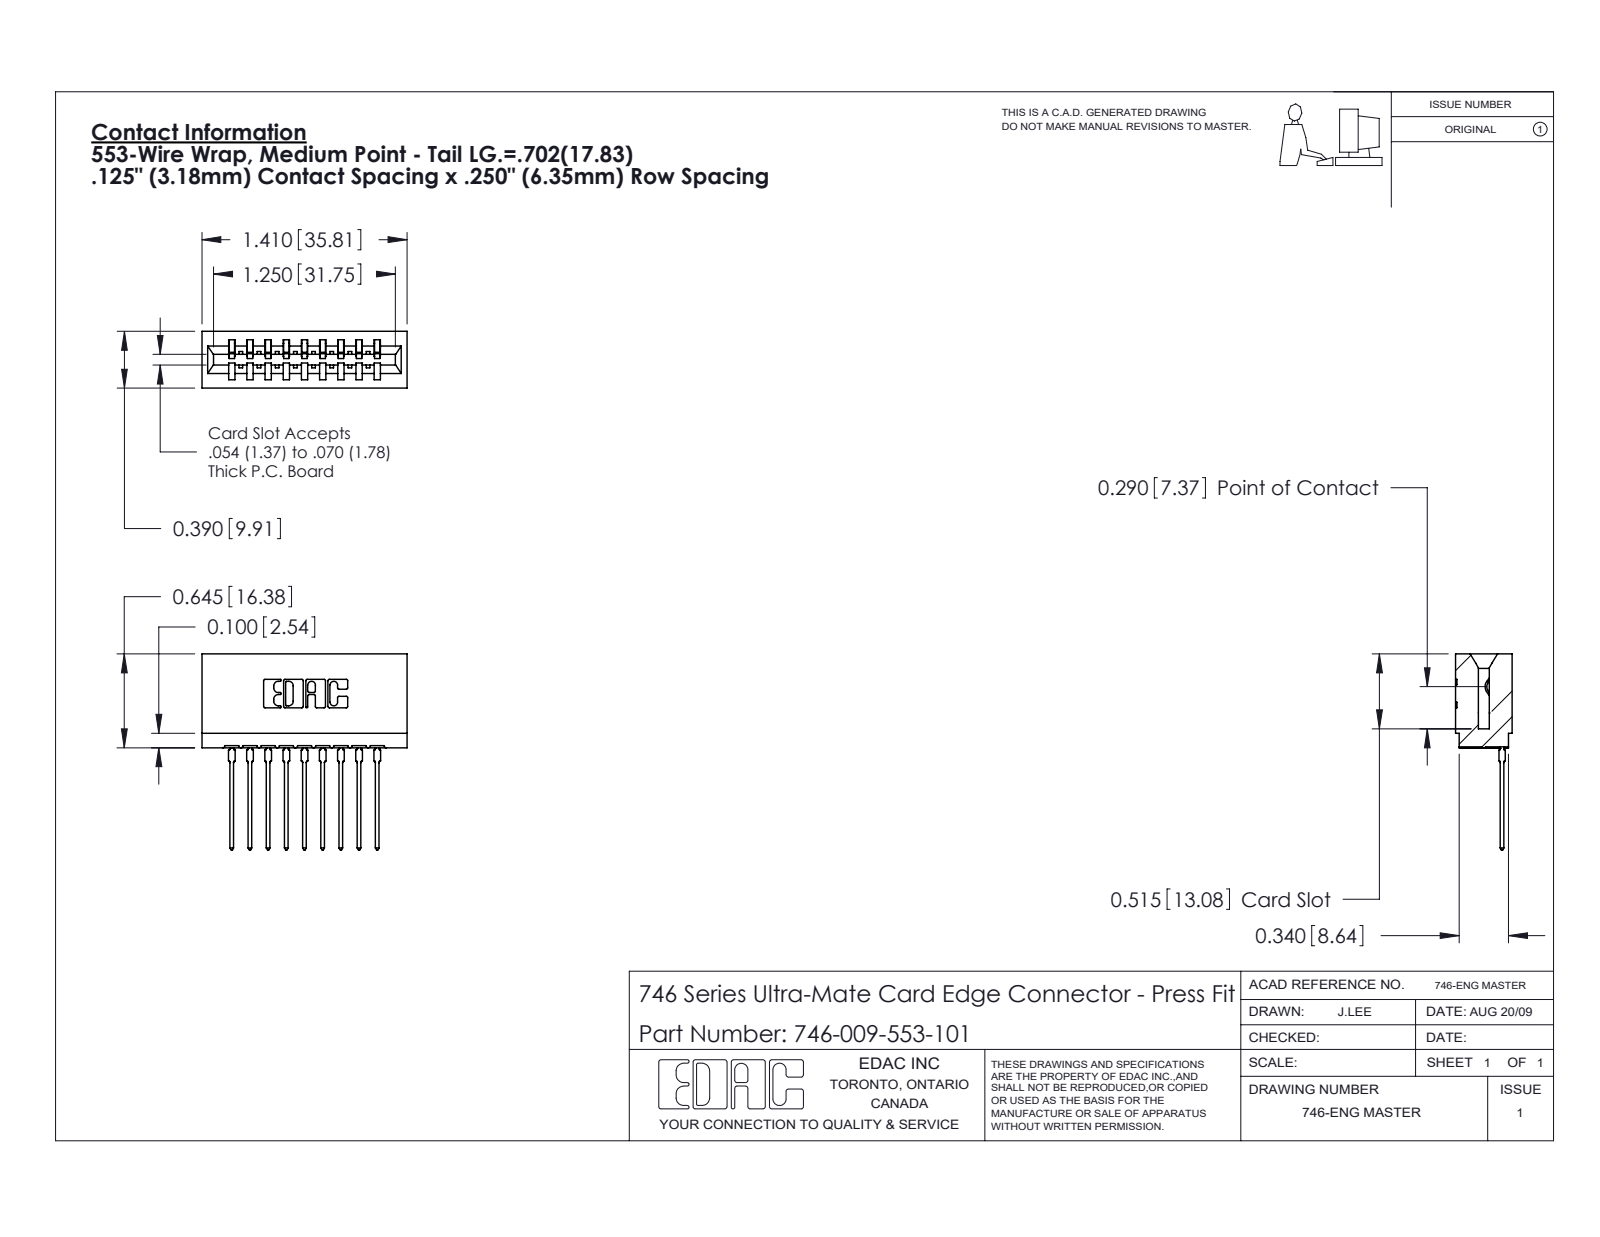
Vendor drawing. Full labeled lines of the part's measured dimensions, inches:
Part name (STEP PRODUCT): 746 Part_.515 Slot Depth - 01; 746-009-553-101; 746-292-001_553
STEP written by: SolidWorks 2020 (CONFIG_CONTROL_DESIGN)
Units: inches
Bodies: 10 solids, 1069 faces (622 planar, 213 cylindrical, 234 other)
Overall size (bounding box): 1.41 × 1.346 × 0.39
Volume: 0.244 in³ · Surface area: 8.591 in²
Partial cylindrical surfaces — rounded edges, fillets, slot ends (radius × count): R0.01 ×22, R0.021 ×18, R0.015 ×10, R0.007 ×6, R0.031 ×6, R0.005 ×4, R0.011 ×4, R0.026 ×3
Main face-to-face distances: 0.25, 0.5, 0.333, 0.042, 0.125, 0.125, 0.057, 0.292, 0.208, 0.083
